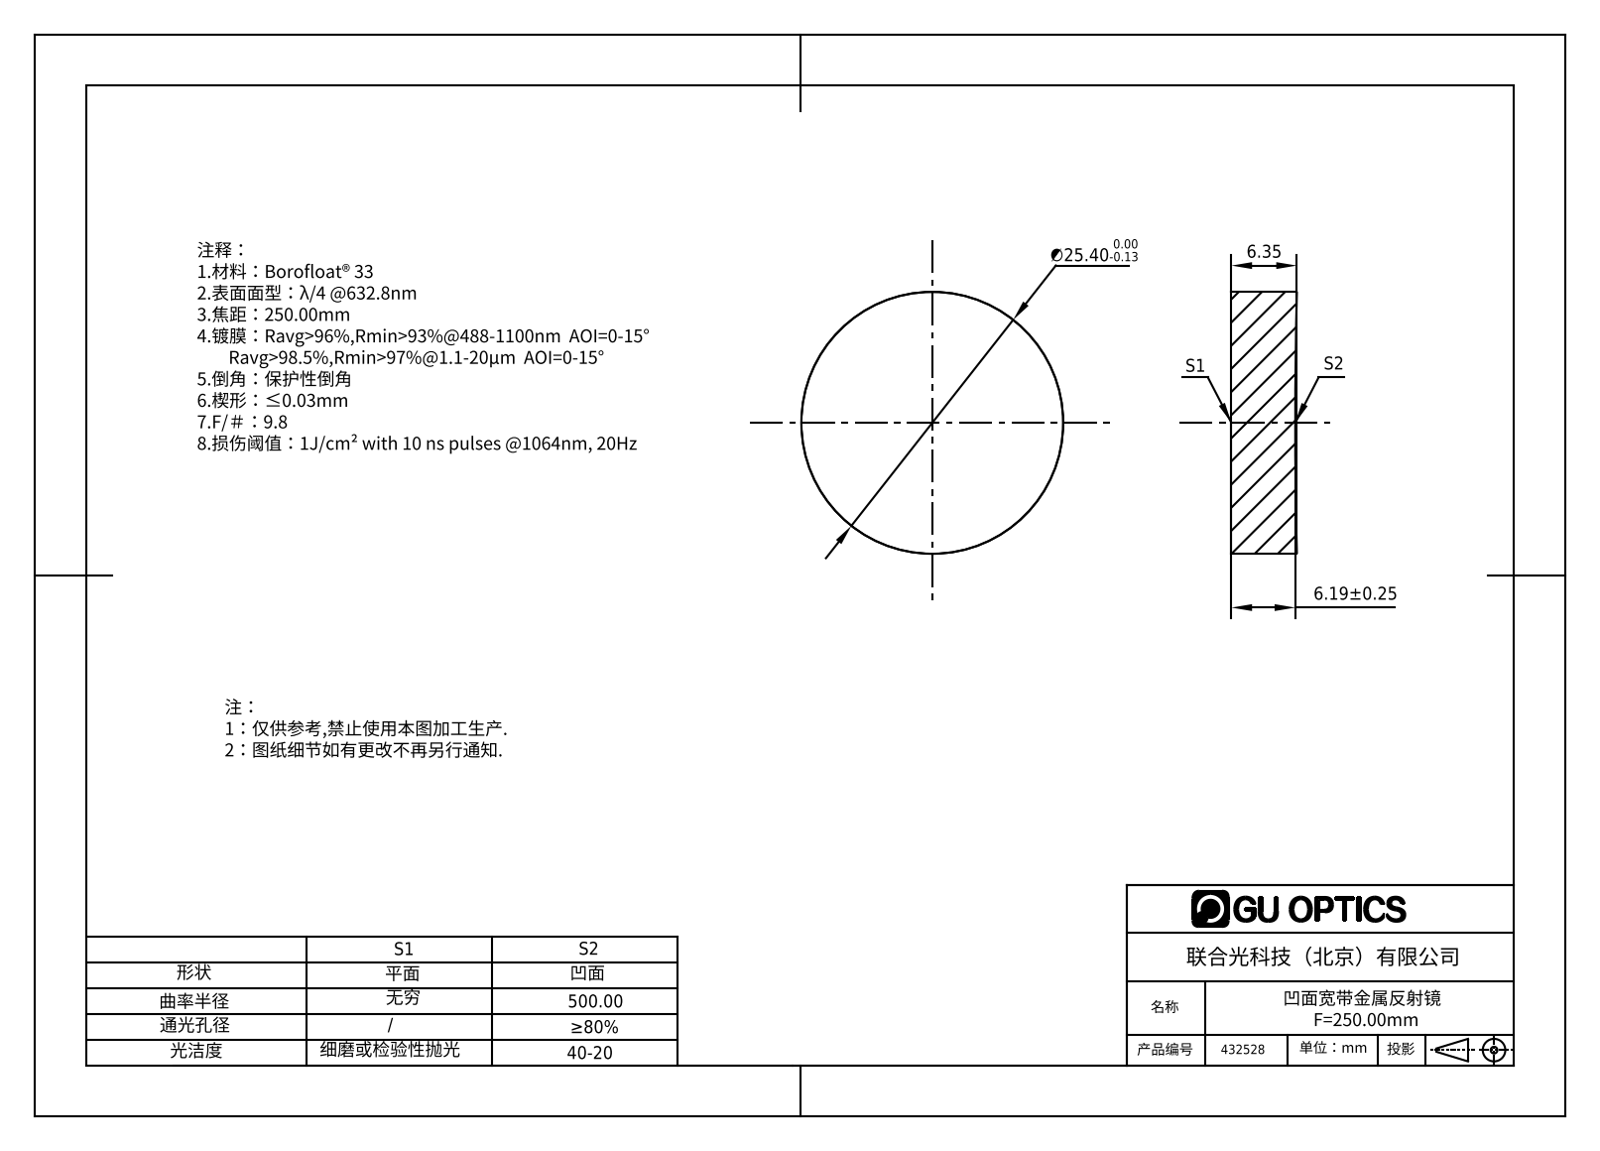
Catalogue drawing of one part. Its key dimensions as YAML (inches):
part_name: "432518"
step_written_by: "SolidWorks 2016 (AUTOMOTIVE_DESIGN)"
units: inches
bodies: {solids: 1, faces: 5, planar: 1, cylindrical: 2, other: 2}
overall_size: [1, 1, 0.25]
volume: 0.194
surface_area: 2.356
round_bosses_or_shafts:
  - {diameter: 1, count: 1}
